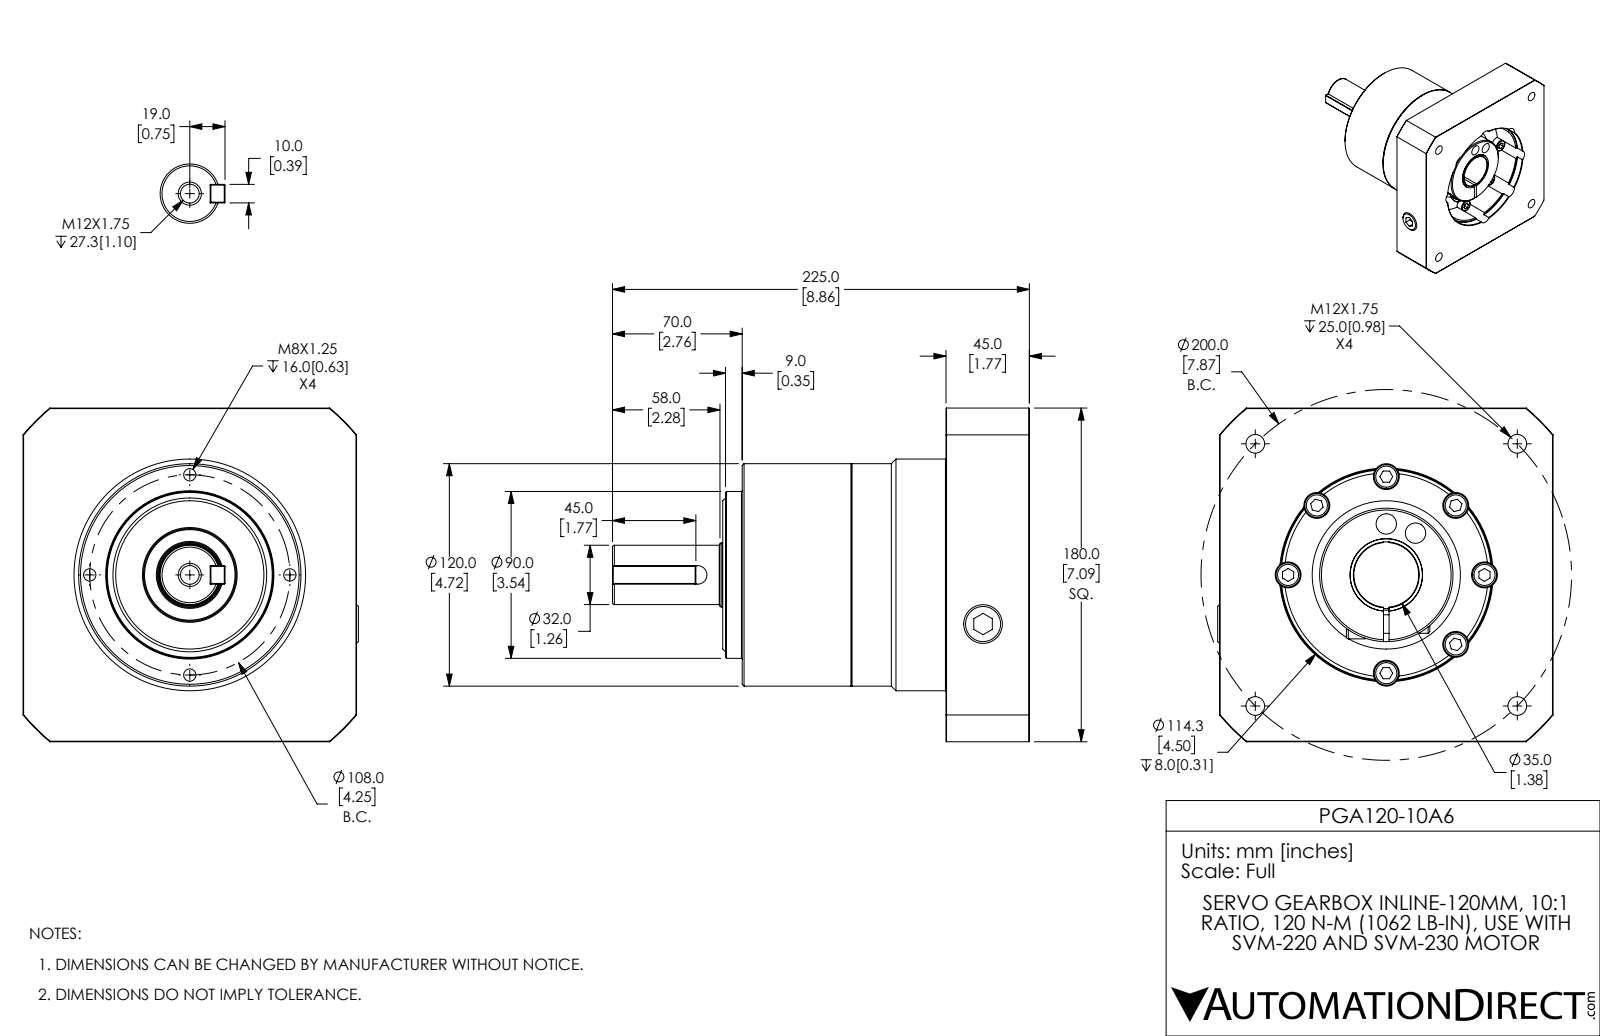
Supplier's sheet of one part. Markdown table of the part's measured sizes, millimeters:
| quantity | value |
| --- | --- |
| part name | PGA120-10A6 |
| STEP written by | SolidWorks 2019 (CONFIG_CONTROL_DESIGN) |
| units | millimeters |
| bodies | 1 solid, 382 faces (149 planar, 107 cylindrical, 126 other) |
| overall size | 225 × 181 × 180 |
| volume | 2 445 000 mm³ |
| surface area | 194 300 mm² |
| round holes (diameter × count) | 14 × 7, 10.1 × 5, 6.7 × 4, 11 × 3, 17.5 × 1, 35 × 1, 80 × 1 |
| round bosses / shafts (diameter × count) | 13 × 7, 125 × 1, 120 × 1, 90 × 1, 72 × 1, 39 × 1, 38 × 1, 32 × 1 |
| partial cylindrical surfaces (radius × count) | 4.2 × 1, 5 × 1, 55 × 1, 57.2 × 1, 117.5 × 1 |
| main face-to-face distances | 45, 180, 9, 119, 155, 110, 36, 10.5, 165.5, 120.5 |
| hole center spacings | 72.7, 72.9, 75.7, 142.5, 143.4, 53, 40.6, 41 |
